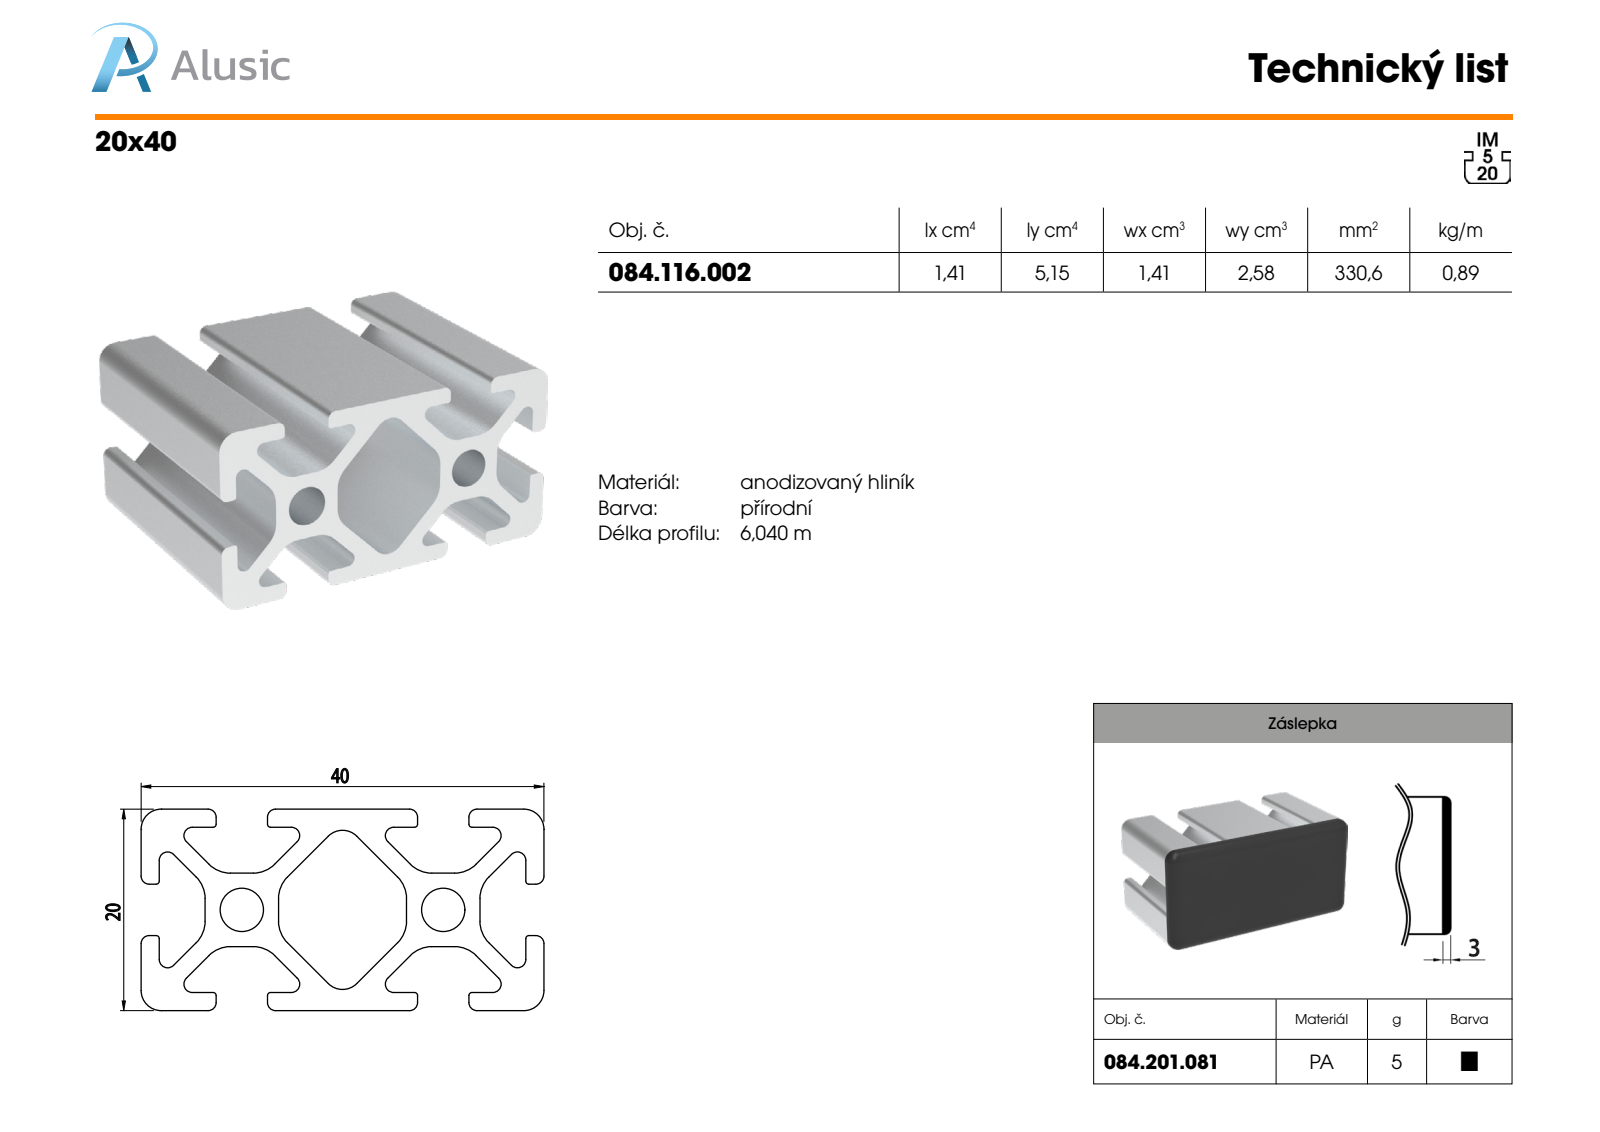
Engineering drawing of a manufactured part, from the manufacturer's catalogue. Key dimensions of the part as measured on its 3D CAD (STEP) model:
Part name (STEP PRODUCT): 084.201.081
STEP written by: SolidWorks 2016 (CONFIG_CONTROL_DESIGN)
Units: millimetres
Bodies: 1 solid, 87 faces (31 planar, 40 cylindrical, 16 other)
Overall size (bounding box): 40 × 20 × 7.5
Volume: 1 726 mm³ · Surface area: 2 102 mm²
Round holes (diameter × count): ⌀6.5 ×2
Round bosses / shafts (diameter × count): ⌀8.5 ×2
Partial cylindrical surfaces — rounded edges, fillets, slot ends (radius × count): R2 ×8, R0.25 ×6, R1 ×4, R2.3 ×2
Main face-to-face distances: 2, 2.5, 0.5, 1.2, 20, 9.4, 10.6, 1.5, 7.9, 9.1
Hole centre spacings: 20
